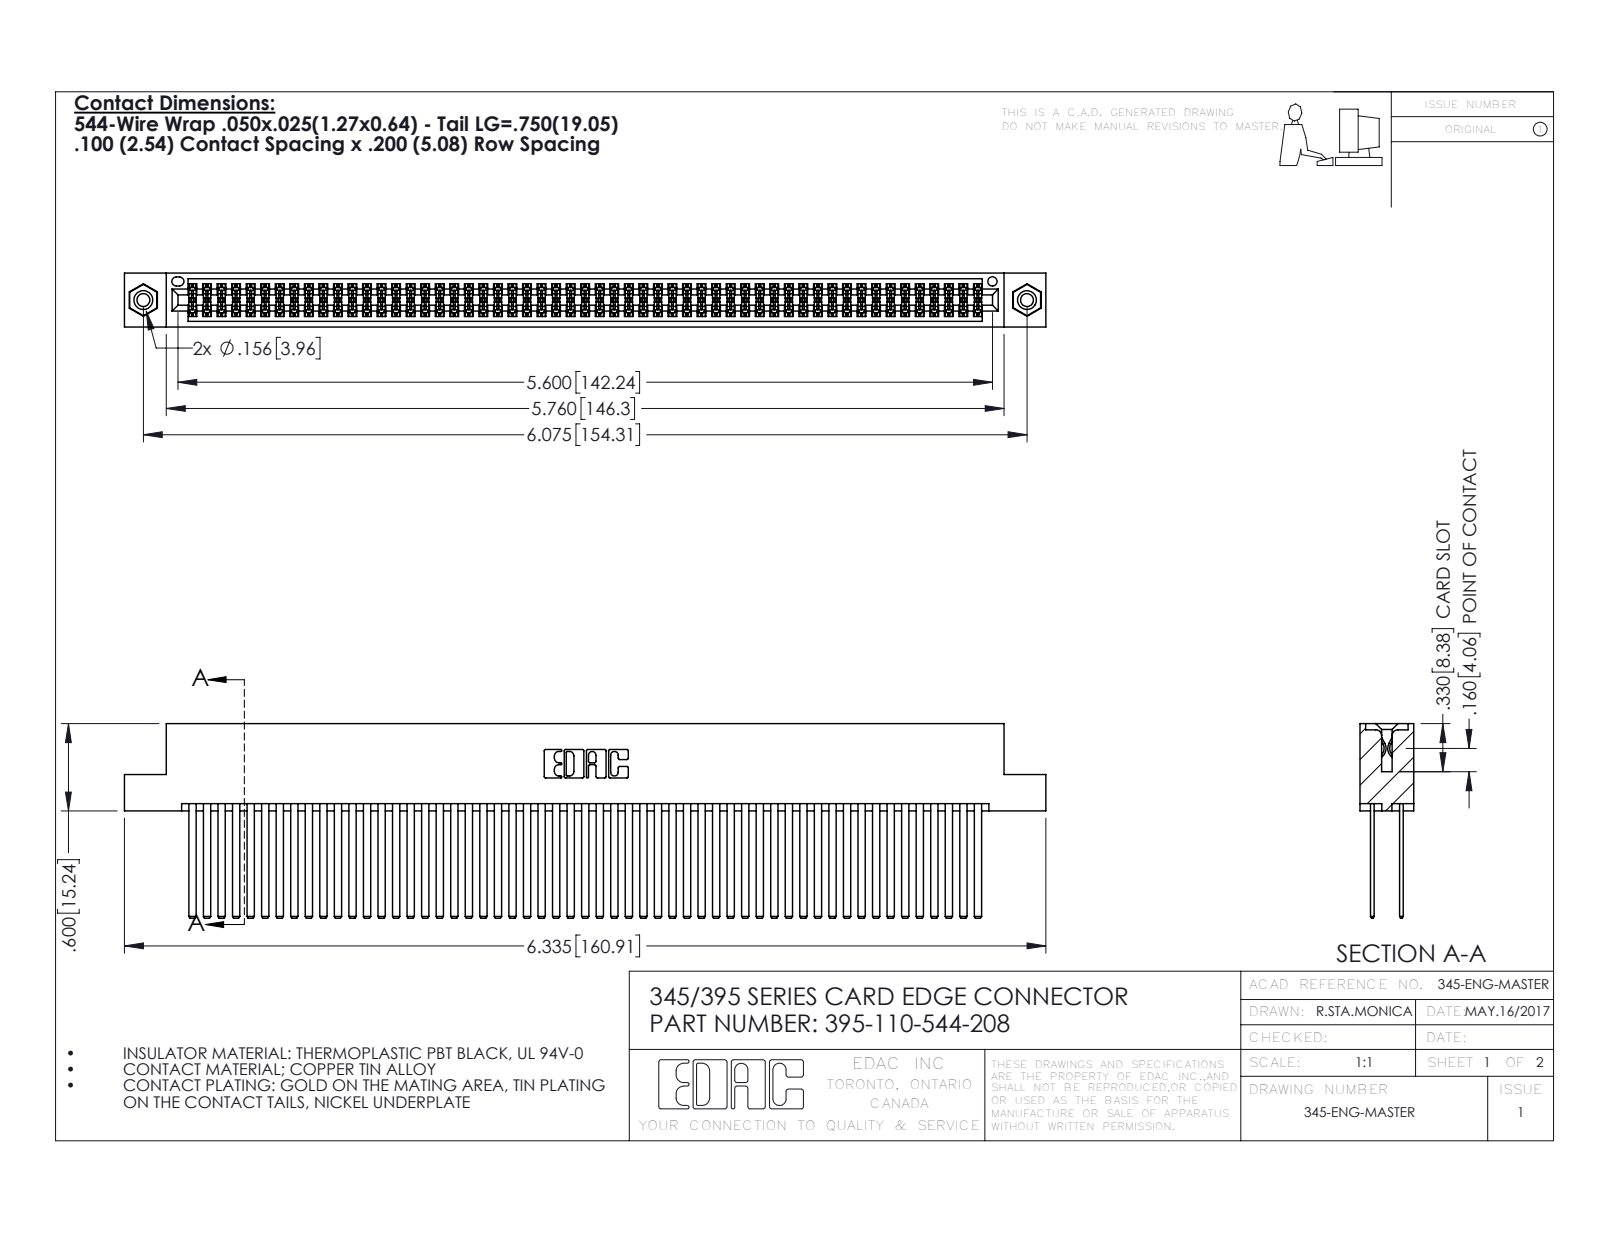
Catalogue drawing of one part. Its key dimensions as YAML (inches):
part_name: "345-292-001_345-293-144; 345-250-001_345-250-003-102; 395-110-544-208; 345 Part_Flush Mounting Lugs - 0.156 Dia-TI"
step_written_by: "SolidWorks 2016 (CONFIG_CONTROL_DESIGN)"
units: inches
bodies: {solids: 113, faces: 5026, planar: 3302, cylindrical: 1708, other: 16}
overall_size: [6.335, 1.337, 0.37]
volume: 1.055
surface_area: 47.02
round_holes:
  - {diameter: 0.089, count: 2}
  - {diameter: 0.125, count: 2}
  - {diameter: 0.156, count: 2}
  - {diameter: 0.064, count: 1}
round_bosses_or_shafts:
  - {diameter: 0.155, count: 2}
partial_cylinders:
  - {radius: 0.006, count: 165}
  - {radius: 0.01, count: 22}
  - {radius: 0.007, count: 6}
  - {radius: 0.031, count: 6}
  - {radius: 0.026, count: 3}
  - {radius: 0.014, count: 2}
  - {radius: 0.019, count: 2}
  - {radius: 0.022, count: 2}
face_to_face_distances: [0.2, 0.025, 0.072, 0.098, 0.272, 0.298, 0.225, 0.175, 0.37, 0.05]
hole_center_spacings: [0.27, 5.839, 6.075]
